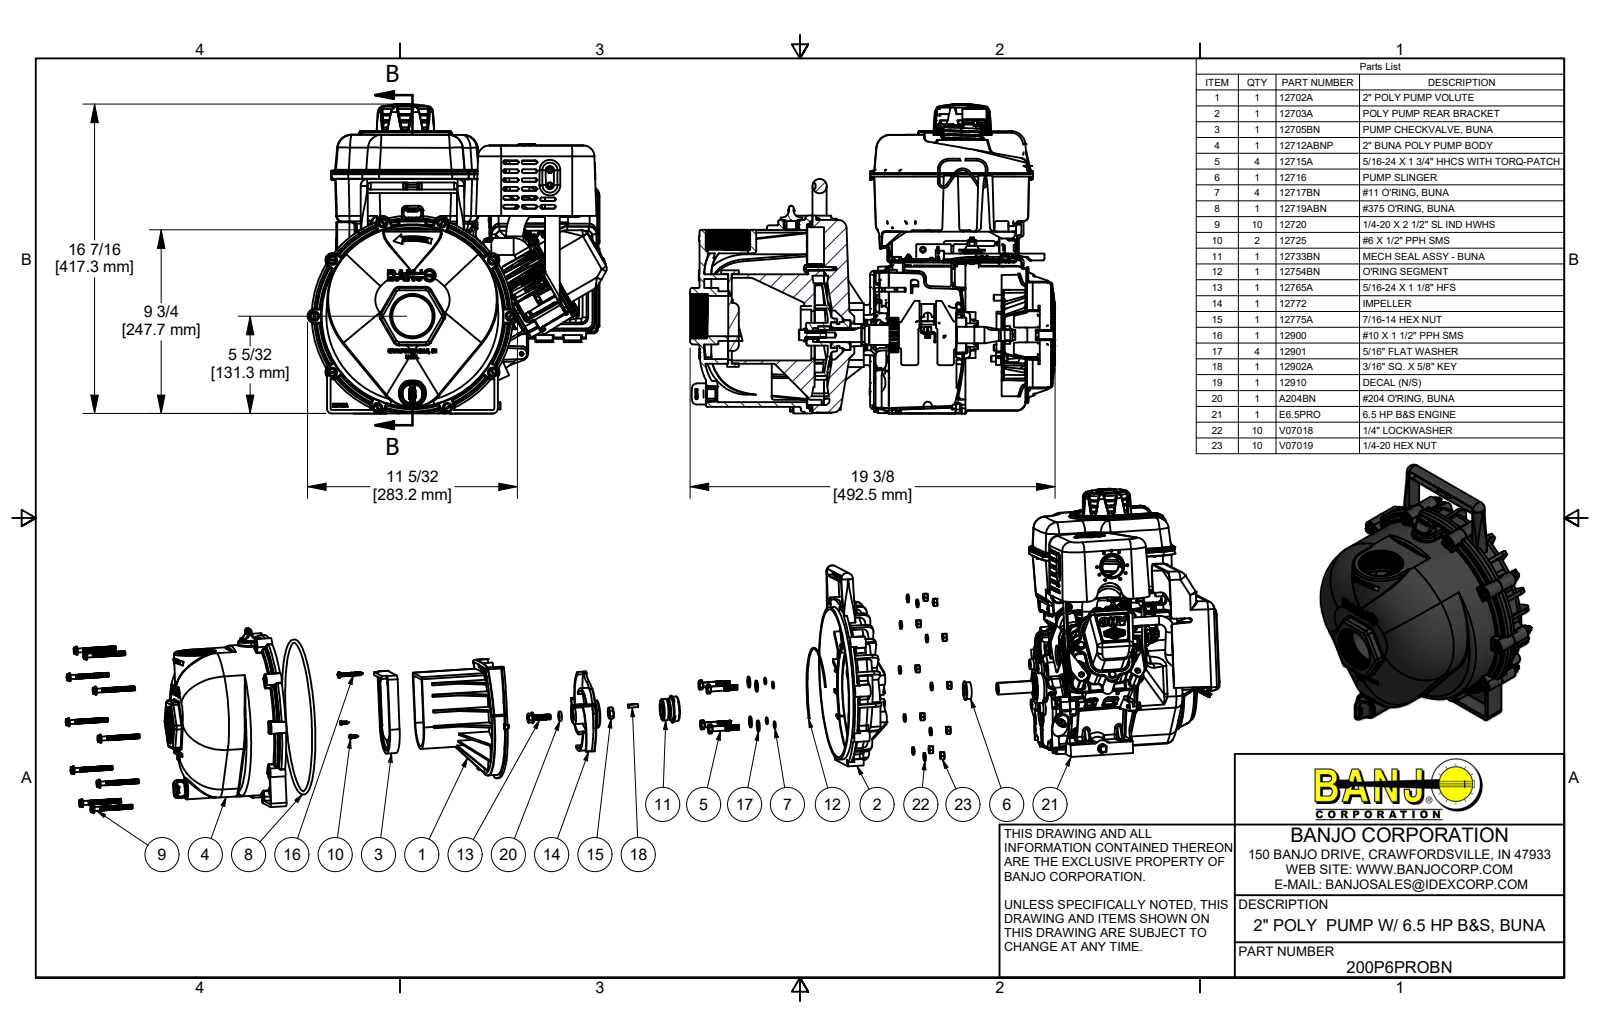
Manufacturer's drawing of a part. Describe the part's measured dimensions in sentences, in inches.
The part is named "200P6PROBN; 12703A; 12712ABNP; X12712A (+8 more)". Its 3-D file was written by "Autodesk Inventor 2019 (AUTOMOTIVE_DESIGN)". It is 84 solids with 20052 faces: 5397 planar, 5553 cylindrical and 9102 other. Overall it measures 20.339 by 17.802 by 15.901 inches. Its volume is 172.8 cubic inches and its surface area 4 993 square inches. Round holes: 13 of diameter 0.25, 11 of diameter 0.27, 10 of diameter 0.196, 10 of diameter 0.252, 9 of diameter 0.138, 7 of diameter 0.14, 7 of diameter 0.22, 6 of diameter 0.319, 5 of diameter 0.272, 5 of diameter 0.28, 4 of diameter 0.218, 4 of diameter 0.295. Round bosses or shafts: 80 of diameter 0.276, 14 of diameter 0.25, 12 of diameter 0.5, 10 of diameter 0.52, 10 of diameter 0.489, 8 of diameter 0.19, 6 of diameter 0.276, 6 of diameter 0.192. Partial cylindrical surfaces (rounded edges, fillets, slot ends): 375 of radius 0.06, 371 of radius 0.03, 202 of radius 0.12, 110 of radius 0.25, 109 of radius 0.09, 76 of radius 0.079, 72 of radius 0.061, 71 of radius 0.015. The main face-to-face distances are 0.036, 0.18, 0.039, 0.08, 0.028, 0.2, 0.086, 8.119, 0.047, 2.88. The hole center spacings are 0.984, 5.2, 0.509, 1.902, 1.705, 0.561, 1.392, 1.705.
